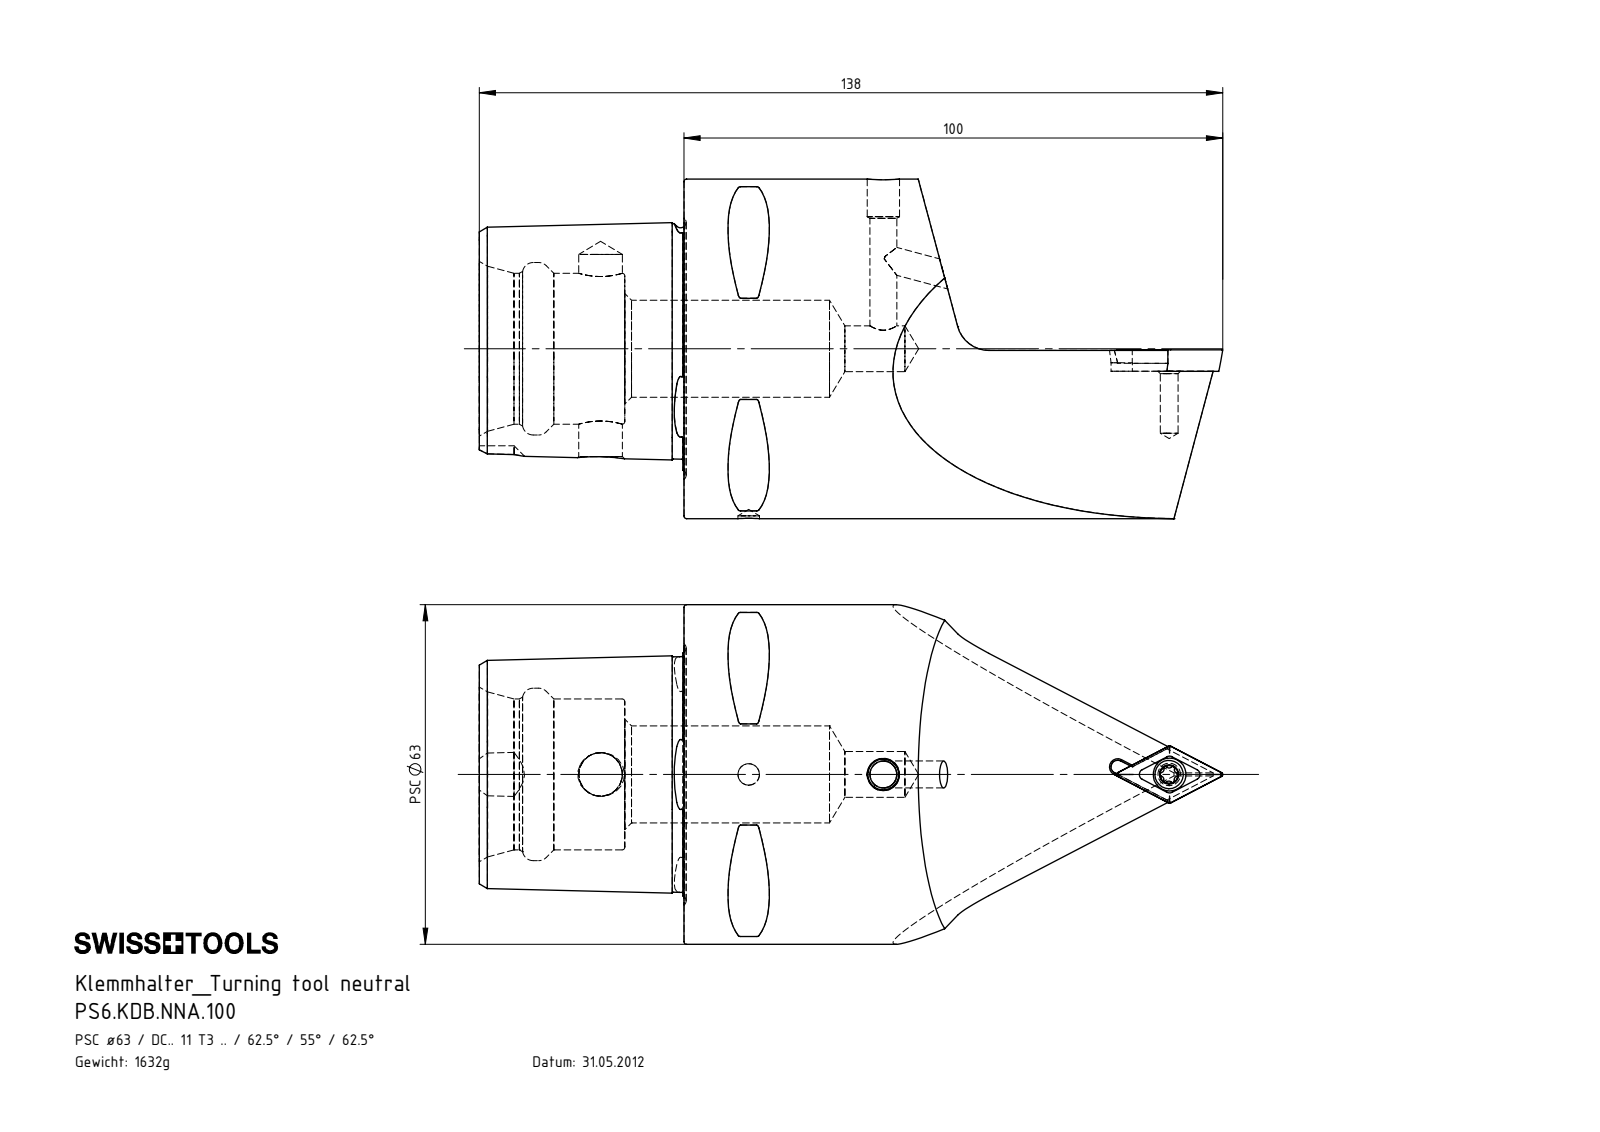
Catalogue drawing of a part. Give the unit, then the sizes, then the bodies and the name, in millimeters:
Units: millimetres
Overall size (bounding box): 138.01 × 63 × 63
Round holes (diameter × count): ⌀5 ×2, ⌀3.3 ×1, ⌀4 ×1, ⌀4.4 ×1, ⌀6.1 ×1, ⌀8.1 ×1, ⌀8.5 ×1, ⌀18 ×1, ⌀28 ×1, ⌀32 ×1
Round bosses / shafts (diameter × count): ⌀63 ×1, ⌀6 ×1, ⌀5.25 ×1, ⌀4 ×1
Partial cylindrical surfaces — rounded edges, fillets, slot ends (radius × count): R0.5 ×8, R0.34 ×6, R0.59 ×6, R6 ×2, R1.25 ×1
Main face-to-face distances: 38, 24.88, 27, 11, 55.8, 3.87, 37.8, 10.8, 3.97, 28.37
Hole centre spacings: 25, 27.5, 52.5, 53.05, 53.15, 78.05, 78.15, 105.55
Volume: 207 678 mm³ · Surface area: 31 172 mm²
Bodies: 5 solids, 267 faces (52 planar, 66 cylindrical, 149 other)
Part name (STEP PRODUCT): KVT_MB_600_060; PS6-KDB.NNA.100_A; WCB-ER2.001.009_A; PS6.KDB.NNA.100 (+1 more)
STEP written by: SolidWorks 2017 (AUTOMOTIVE_DESIGN)
